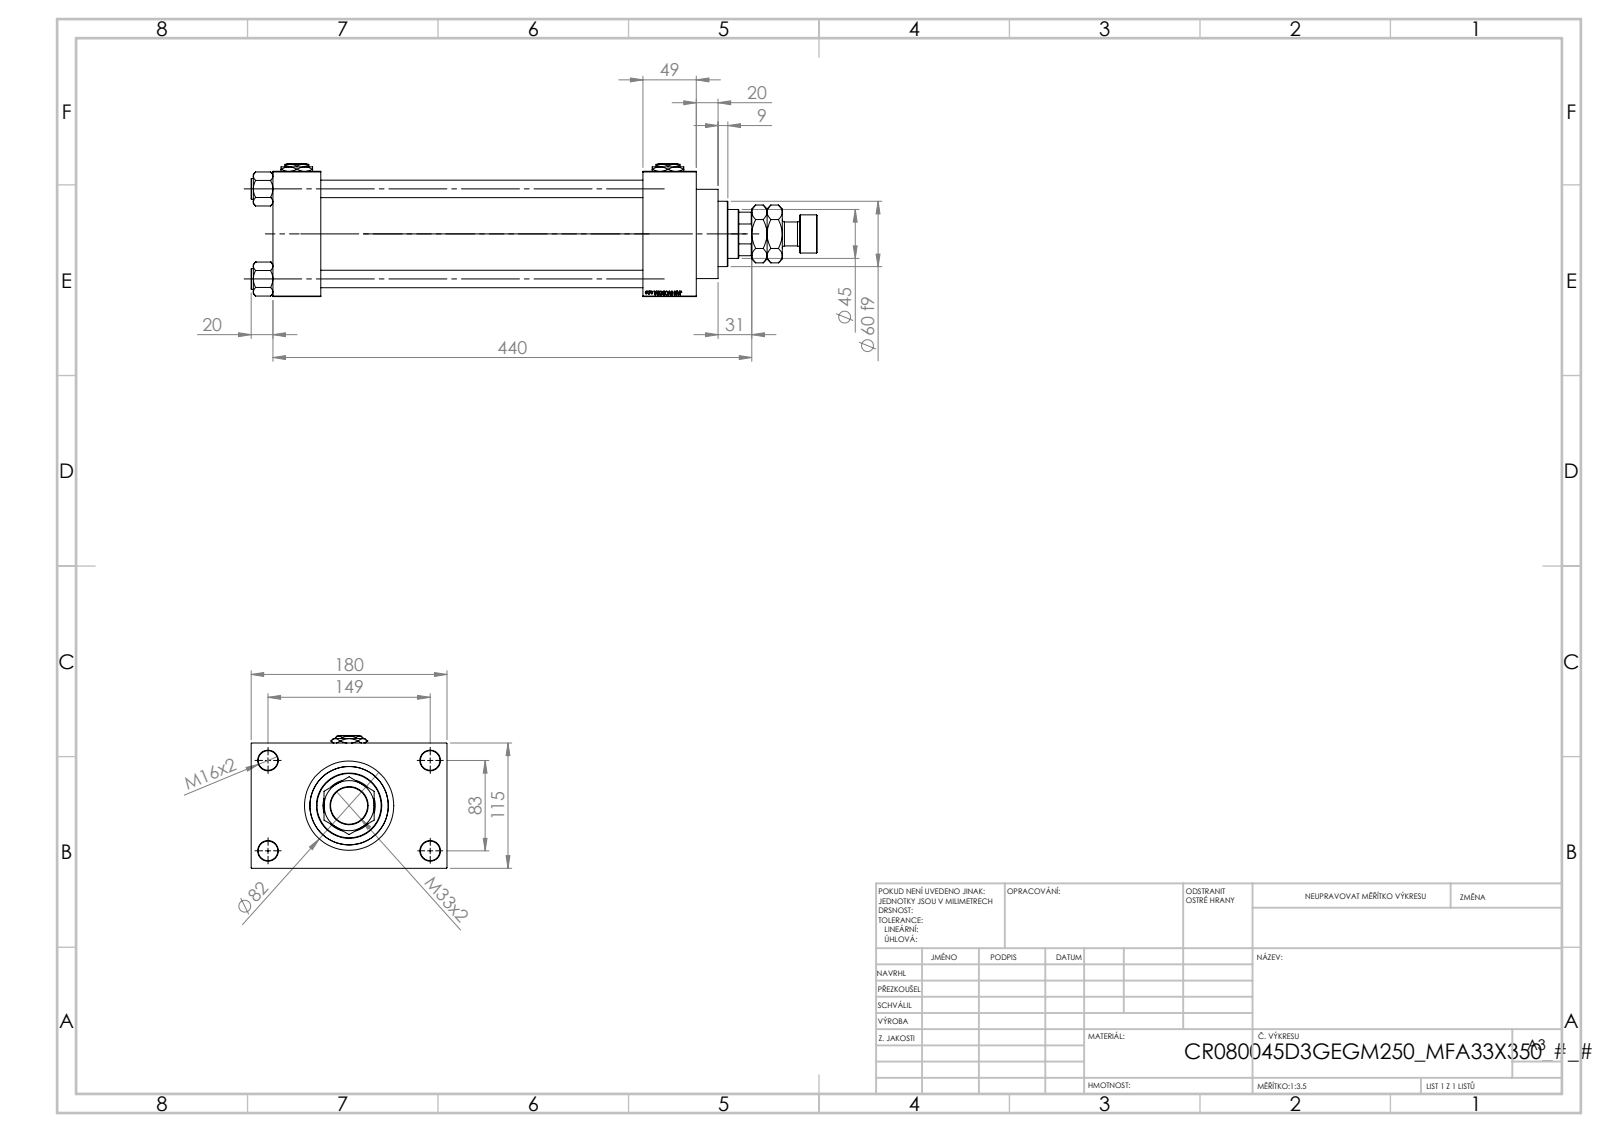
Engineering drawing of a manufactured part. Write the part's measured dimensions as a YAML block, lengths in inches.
part_name: "NUT_M5_D; MFA; Zatka_pro_OIL_PORT; V215CR_D_TYCINKA (+3 more)"
step_written_by: "SolidWorks 2019 (CONFIG_CONTROL_DESIGN)"
units: inches
bodies: {solids: 14, faces: 1305, planar: 609, cylindrical: 104, other: 592}
overall_size: [20.472, 7.087, 4.803]
volume: 171.5
surface_area: 801.3
round_holes:
  - {diameter: 0.63, count: 4}
  - {diameter: 0.709, count: 4}
  - {diameter: 0.276, count: 2}
  - {diameter: 1.041, count: 2}
  - {diameter: 1.378, count: 2}
  - {diameter: 1.24, count: 1}
  - {diameter: 1.772, count: 1}
  - {diameter: 1.89, count: 1}
  - {diameter: 2.402, count: 1}
  - {diameter: 2.835, count: 1}
  - {diameter: 3.15, count: 1}
round_bosses_or_shafts:
  - {diameter: 0.748, count: 4}
  - {diameter: 3.386, count: 1}
  - {diameter: 3.228, count: 1}
  - {diameter: 2.362, count: 1}
  - {diameter: 1.378, count: 1}
  - {diameter: 0.866, count: 1}
partial_cylinders:
  - {radius: 0.866, count: 1}
face_to_face_distances: [4.528, 11.654, 13.583, 1.929, 1.732, 13.386, 15.315, 1.28, 5.807, 7.087]
hole_center_spacings: [1.305, 2.302, 3.256, 3.357, 3.513, 4.561, 5.607, 3.268]
